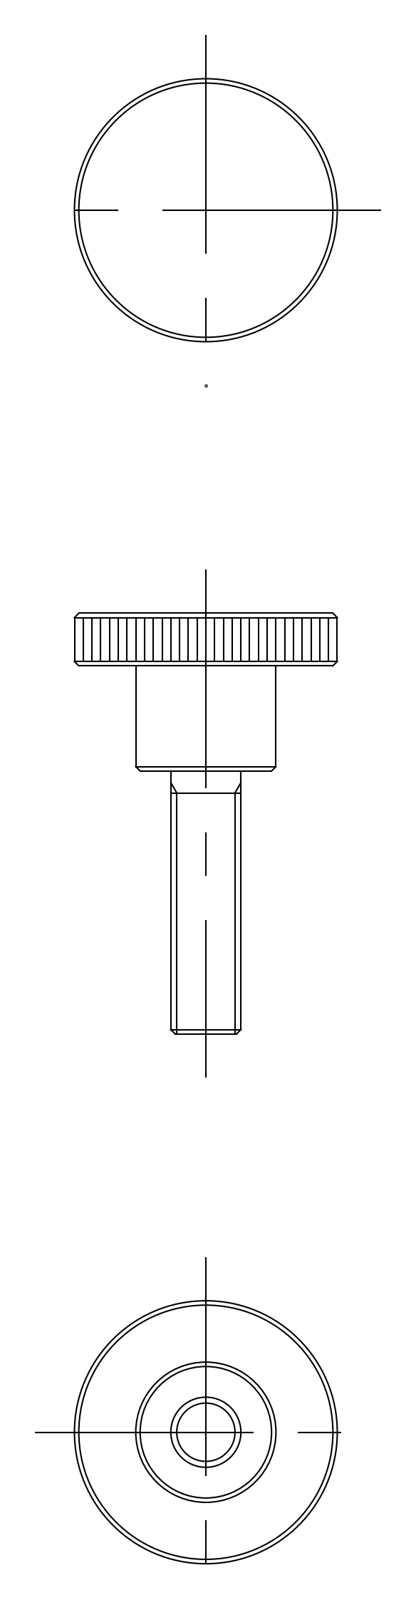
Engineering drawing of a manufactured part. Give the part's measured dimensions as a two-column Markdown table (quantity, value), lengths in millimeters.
| quantity | value |
| --- | --- |
| part name | knob |
| STEP written by | CADfix (AUTOMOTIVE_DESIGN) |
| units | millimeters |
| bodies | 1 solid, 18 faces (0 planar, 0 cylindrical, 18 other) |
| overall size | 48 × 30 × 30 |
| volume | 8 144 mm³ |
| surface area | 3 259 mm² |
